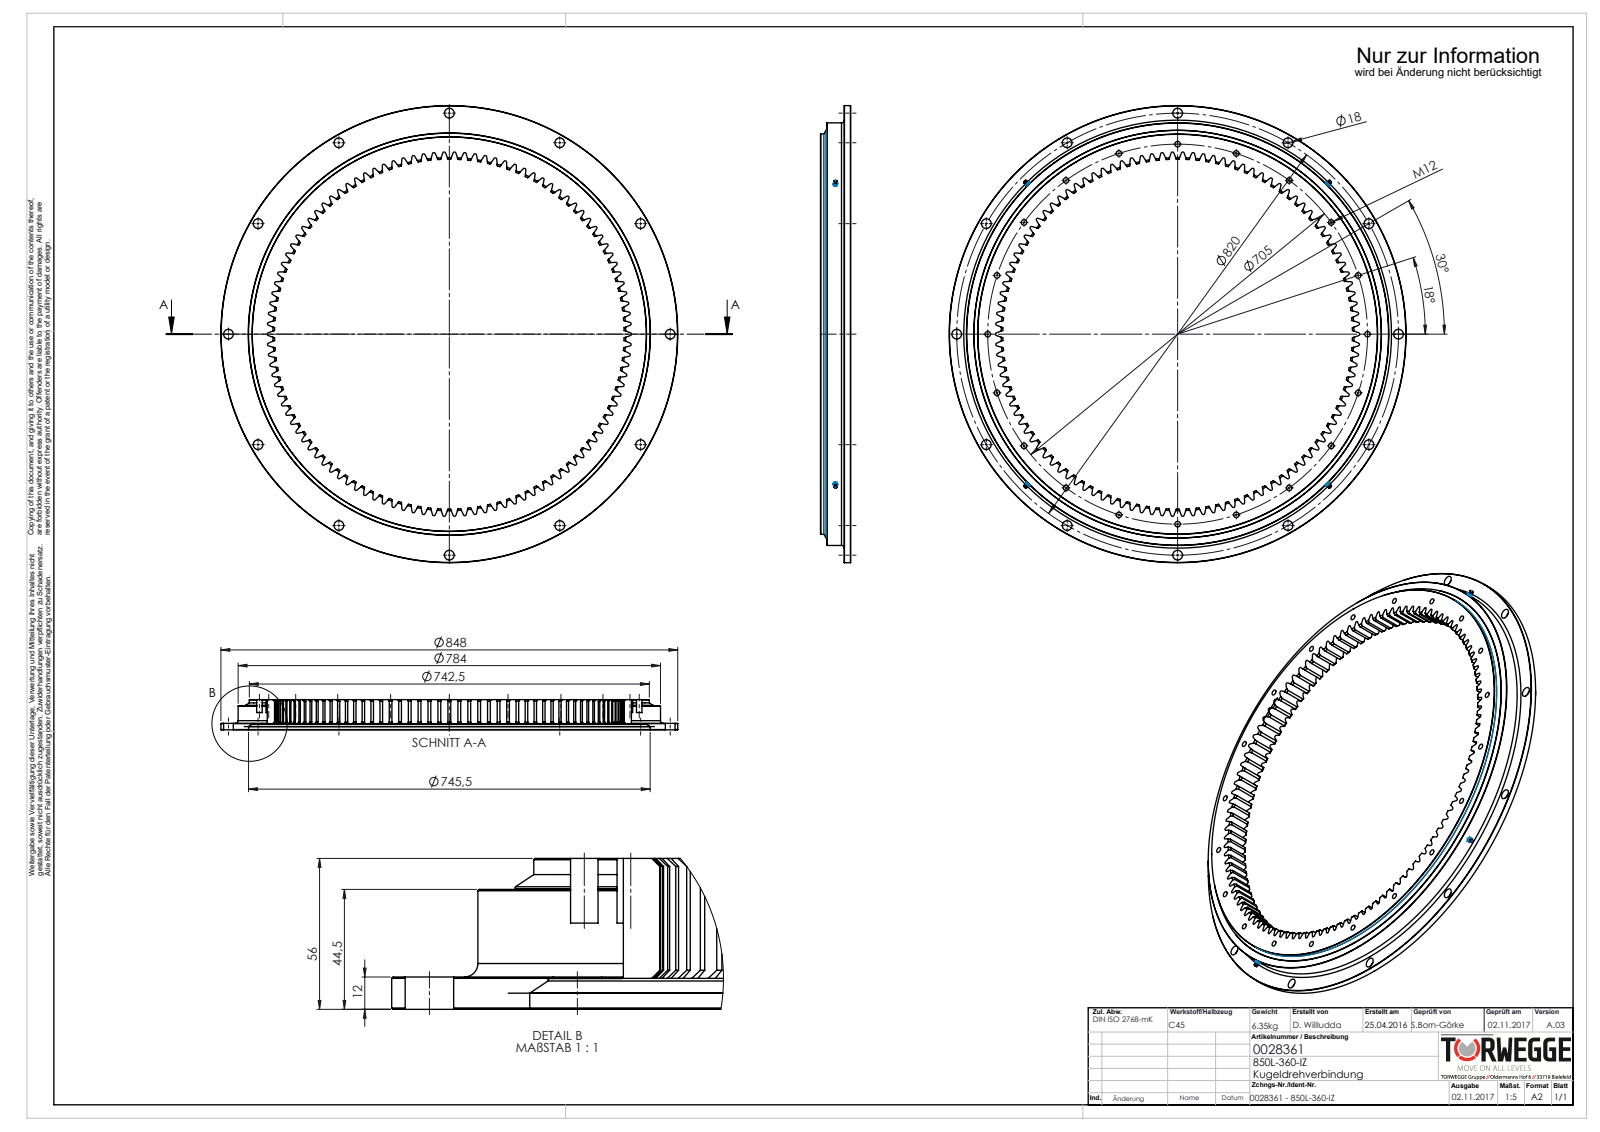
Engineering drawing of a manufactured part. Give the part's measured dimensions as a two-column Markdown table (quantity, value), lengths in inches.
| quantity | value |
| --- | --- |
| part name | 0028361_850L-360-IZ |
| STEP written by | SolidWorks 2016 (AUTOMOTIVE_DESIGN) |
| units | inches |
| bodies | 0 solids, 593 faces (31 planar, 182 cylindrical, 380 other) |
| overall size | 33.386 × 33.386 × 2.205 |
| round holes (diameter × count) | 0.402 × 20, 0.709 × 12, 29.35 × 1 |
| round bosses / shafts (diameter × count) | 33.386 × 1, 30.866 × 1, 29.232 × 1 |
| partial cylindrical surfaces (radius × count) | 12.776 × 1 |
| main face-to-face distances | 0.453, 1.752, 2.205, 1.732, 0.02, 0.472, 0.236, 1.28, 1.299, 1.969 |
| hole center spacings | 19.626, 22.455, 27.414, 16.315, 24.731, 4.342, 8.577, 12.601 |
